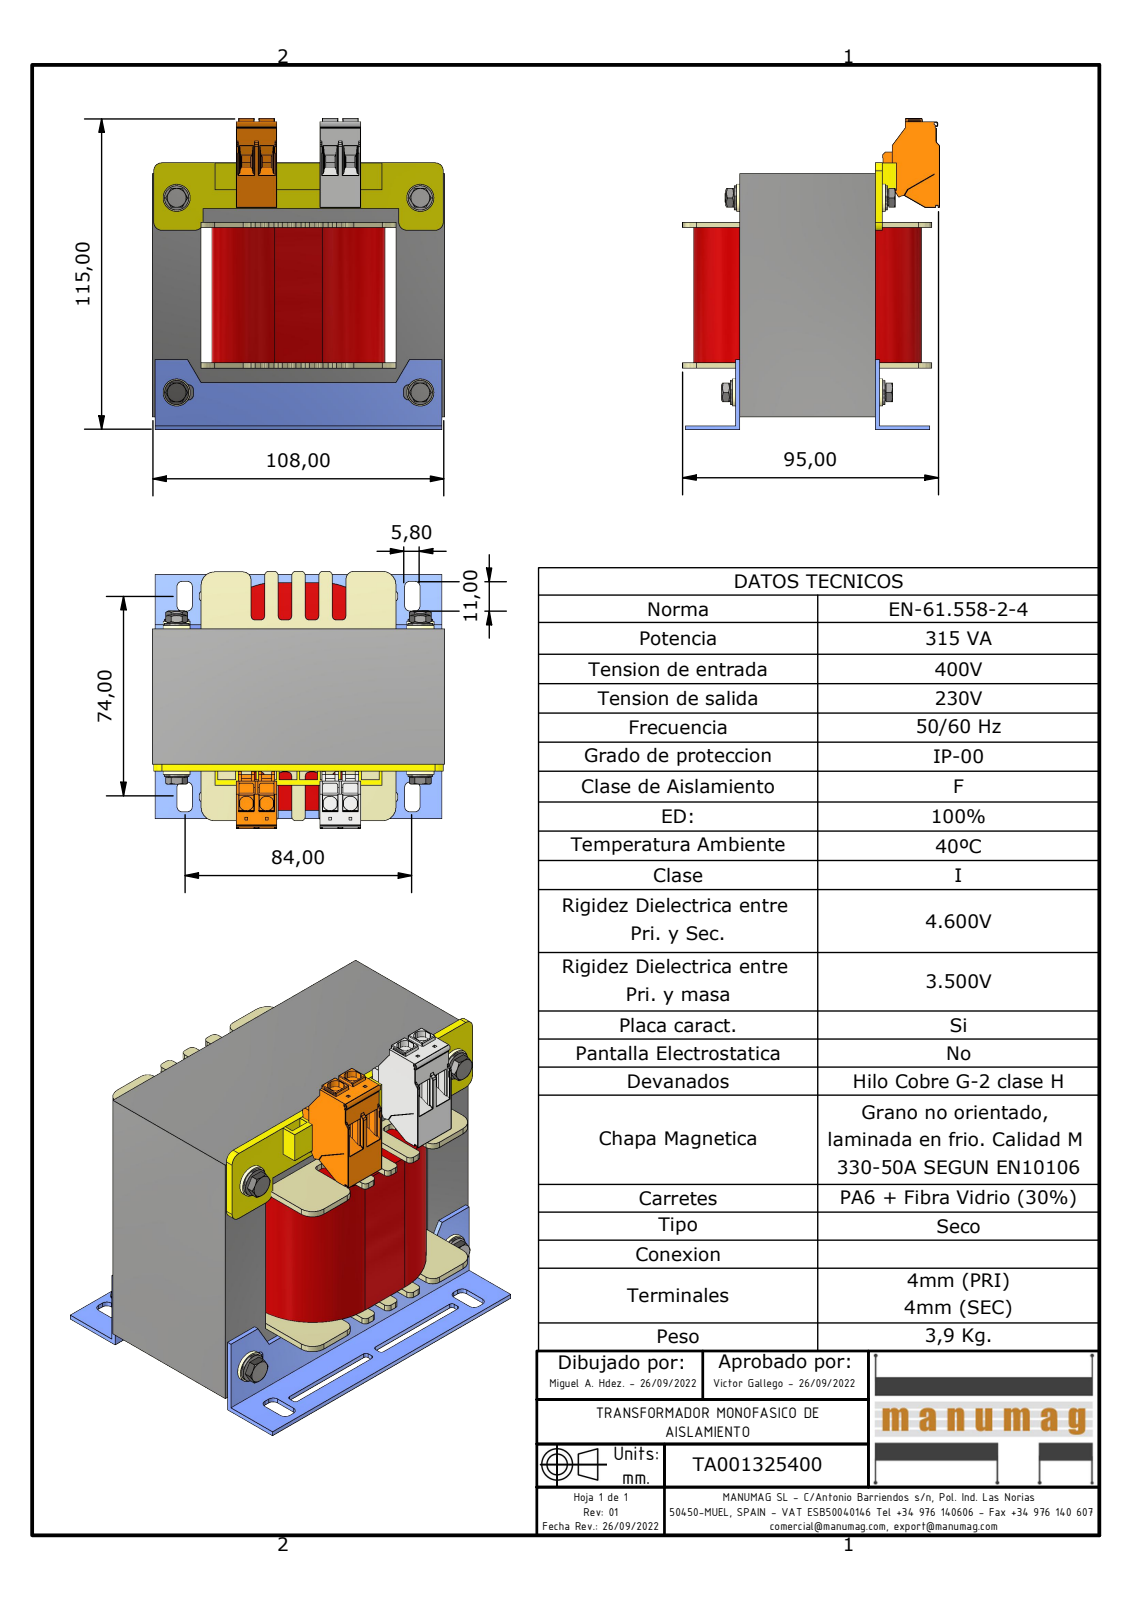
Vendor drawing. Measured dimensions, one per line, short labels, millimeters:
name: TA001325400; EI108 x 90 - 50 (RC36); EI108; AF36DIN (+7 more)
written by: Autodesk Inventor 2023 (AUTOMOTIVE_DESIGN)
unit: mm
bodies: 31 solids, 3835 faces (3043 planar, 550 cylindrical, 242 other)
size: 115.27 × 108 × 94.9
volume: 587 460 mm³; area: 131 594 mm²
holes: 4× ⌀3.24, 4× ⌀4, 4× ⌀4.3, 4× ⌀5.6
bosses: 4× ⌀10, 4× ⌀9, 4× ⌀5.9, 4× ⌀4.9, 4× ⌀3.62
rounds: 160× R0.15, 48× R0.2, 28× R1.5, 24× R2, 20× R1, 12× R0.5, 10× R3, 8× R5
face distances: 18, 72, 50, 36, 54, 90, 1.5, 2, 20, 108
hole spacings: 72, 90, 115.26
